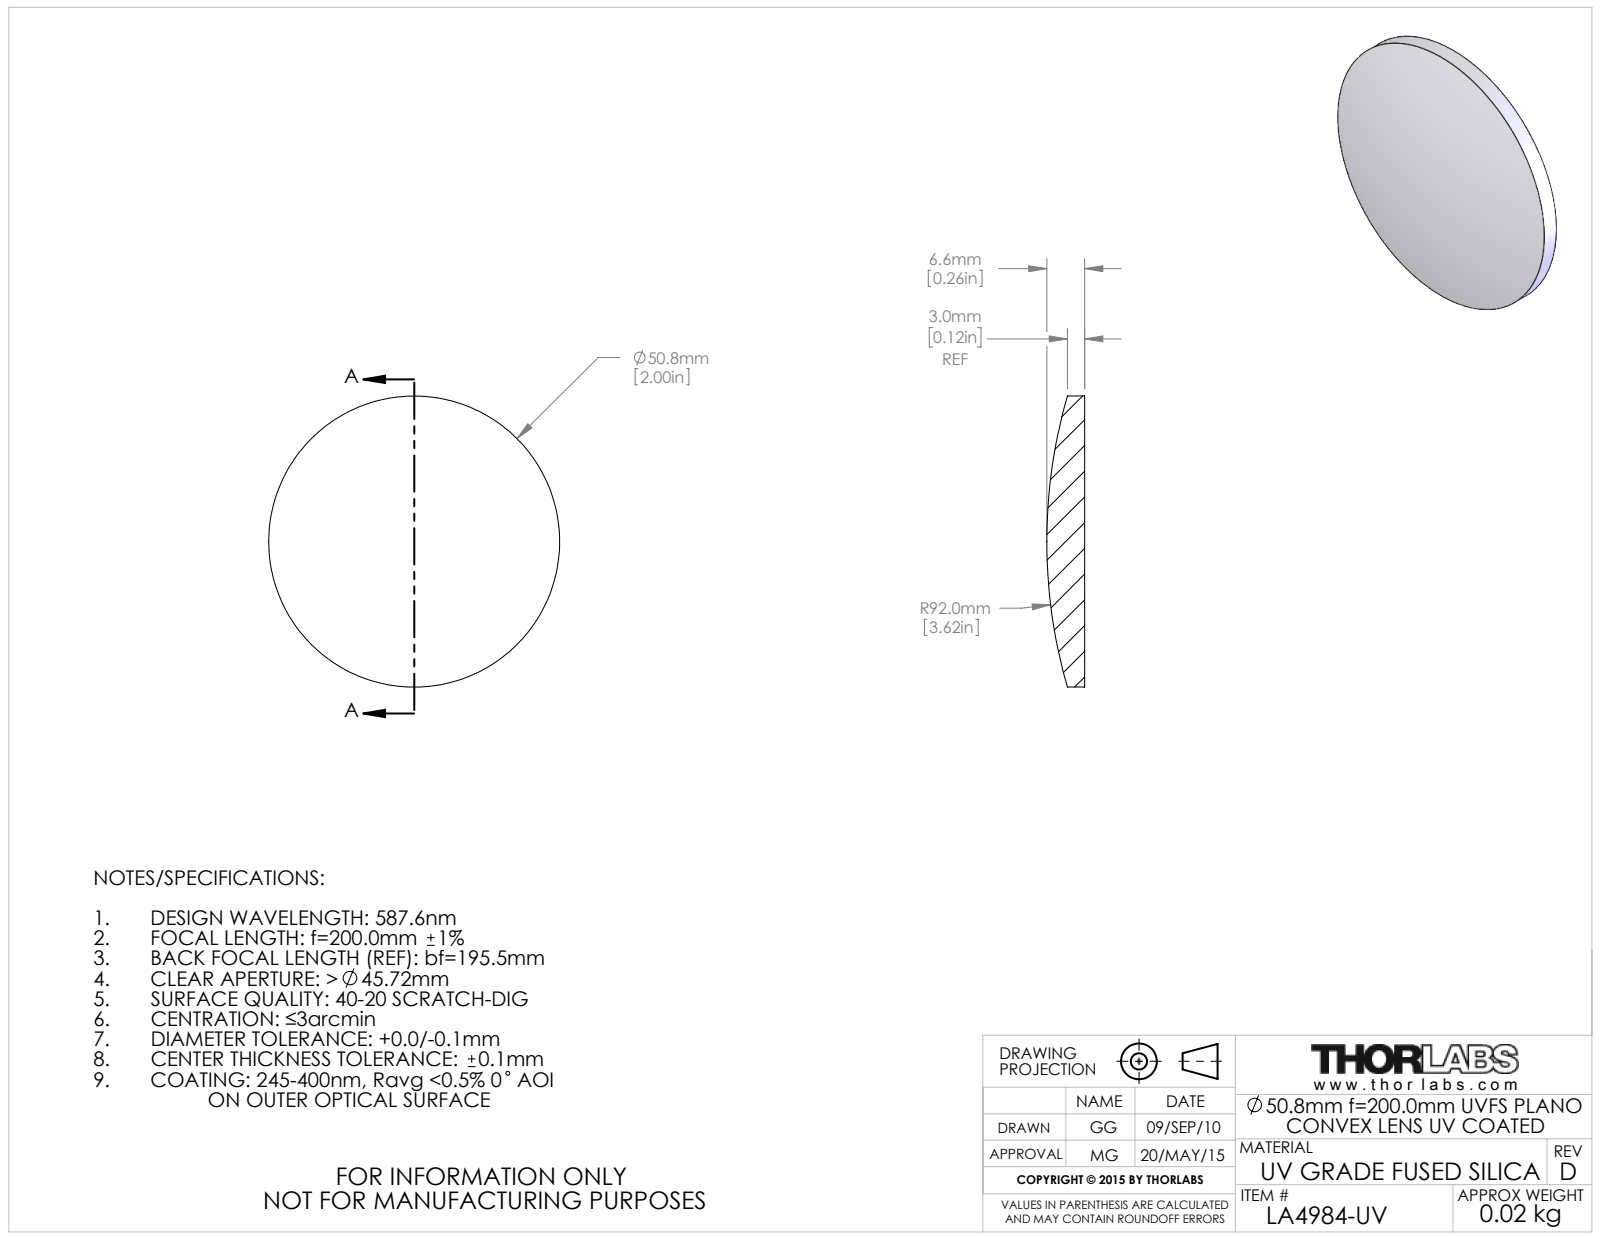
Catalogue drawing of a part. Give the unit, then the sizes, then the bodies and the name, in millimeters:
Units: millimetres
Overall size (bounding box): 50.8 × 50.8 × 6.6
Round bosses / shafts (diameter × count): ⌀50.8 ×1
Volume: 9 745 mm³ · Surface area: 4 571 mm²
Bodies: 1 solid, 7 faces (1 planar, 2 cylindrical, 4 other)
Part name (STEP PRODUCT): 4296-E0W
STEP written by: SolidWorks 2018 (CONFIG_CONTROL_DESIGN)
